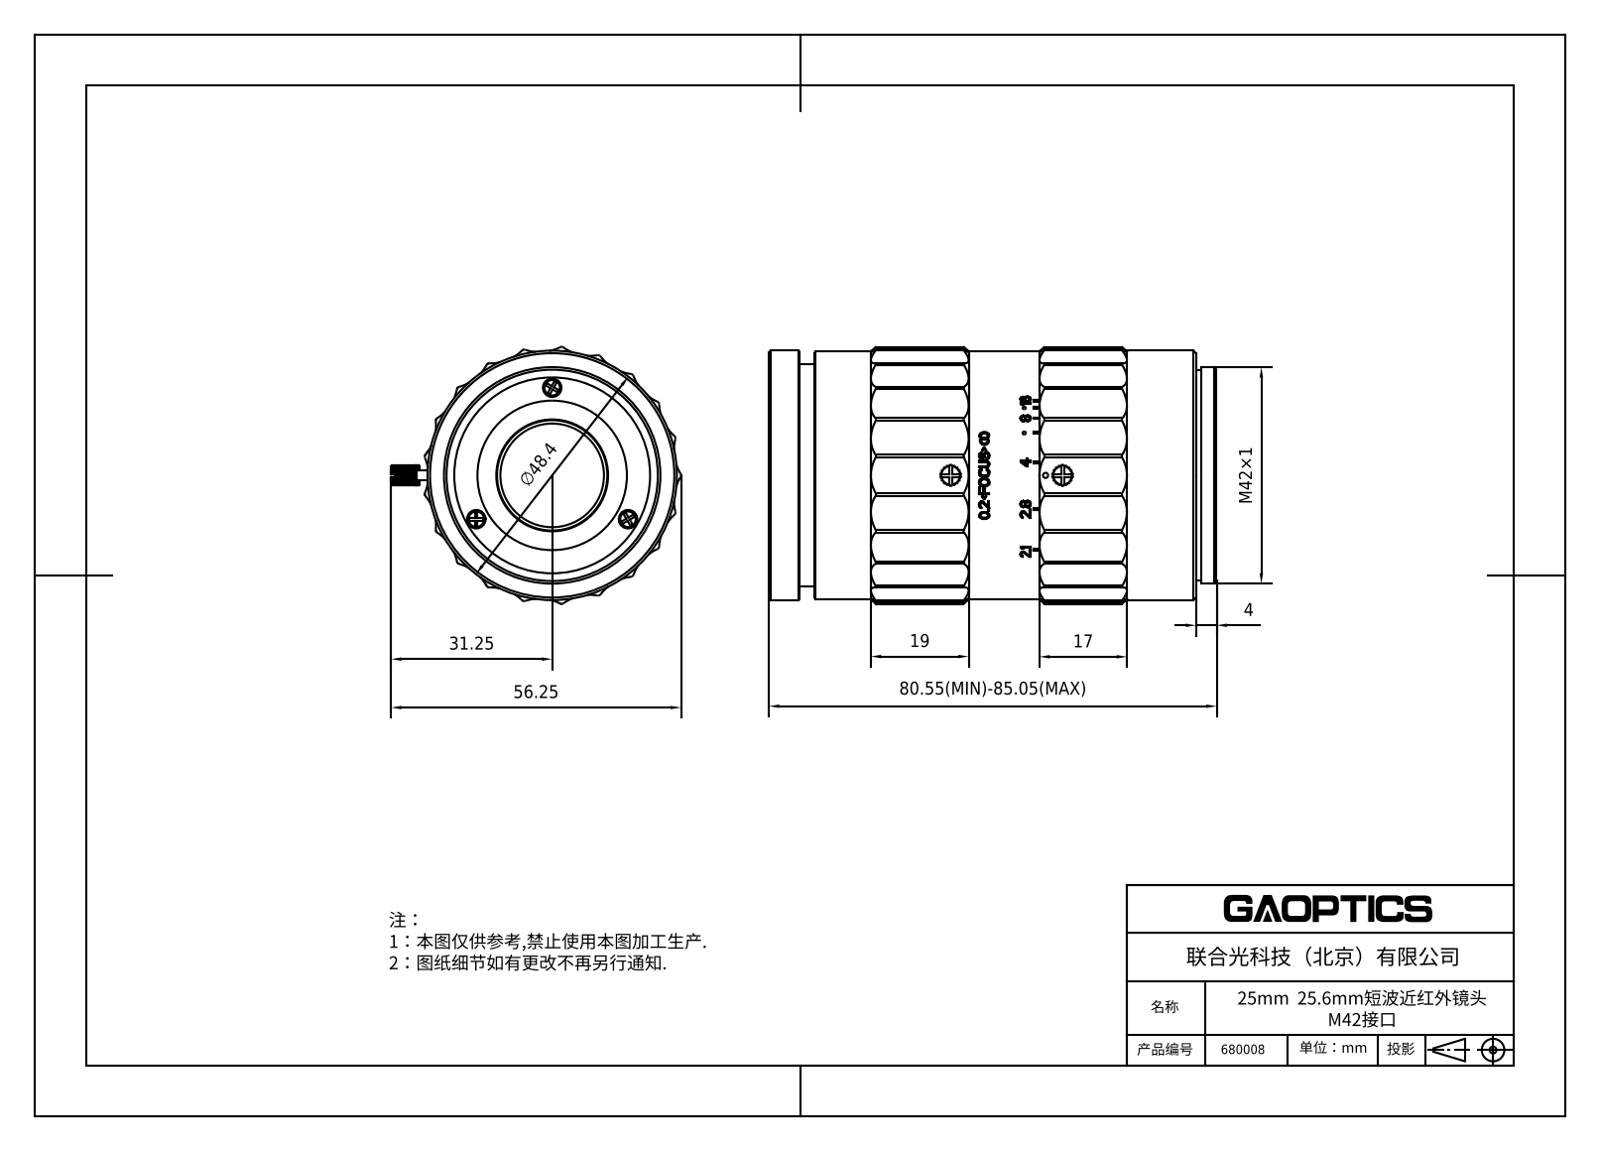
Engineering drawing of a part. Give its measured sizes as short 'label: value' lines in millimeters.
name: 680008
written by: SolidWorks 2020 (CONFIG_CONTROL_DESIGN)
unit: mm
bodies: 5 solids, 2099 faces (1239 planar, 421 cylindrical, 439 other)
size: 86.85 × 56.25 × 49.86
volume: 129 099 mm³; area: 48 362 mm²
holes: 12× ⌀1.6, 3× ⌀2.2, 3× ⌀3.2, 2× ⌀2.4, 1× ⌀1.5, 1× ⌀2.7, 1× ⌀4.5, 1× ⌀29, 1× ⌀32, 1× ⌀34, 1× ⌀34.4, 1× ⌀35.2
bosses: 3× ⌀3.6, 1× ⌀48.4, 1× ⌀48, 1× ⌀43, 1× ⌀42.5, 1× ⌀42, 1× ⌀41.5, 1× ⌀40.8
rounds: 21× R0.6, 21× R9, 8× R2, 6× R1, 2× R1.25, 2× R1.5, 2× R2.25, 1× R1.2
face distances: 50.05, 4, 50, 46.05, 3.95, 13.38, 2.75, 9, 3, 11.75
hole spacings: 18.5, 32.04, 21.72, 37, 8.75, 30.47
